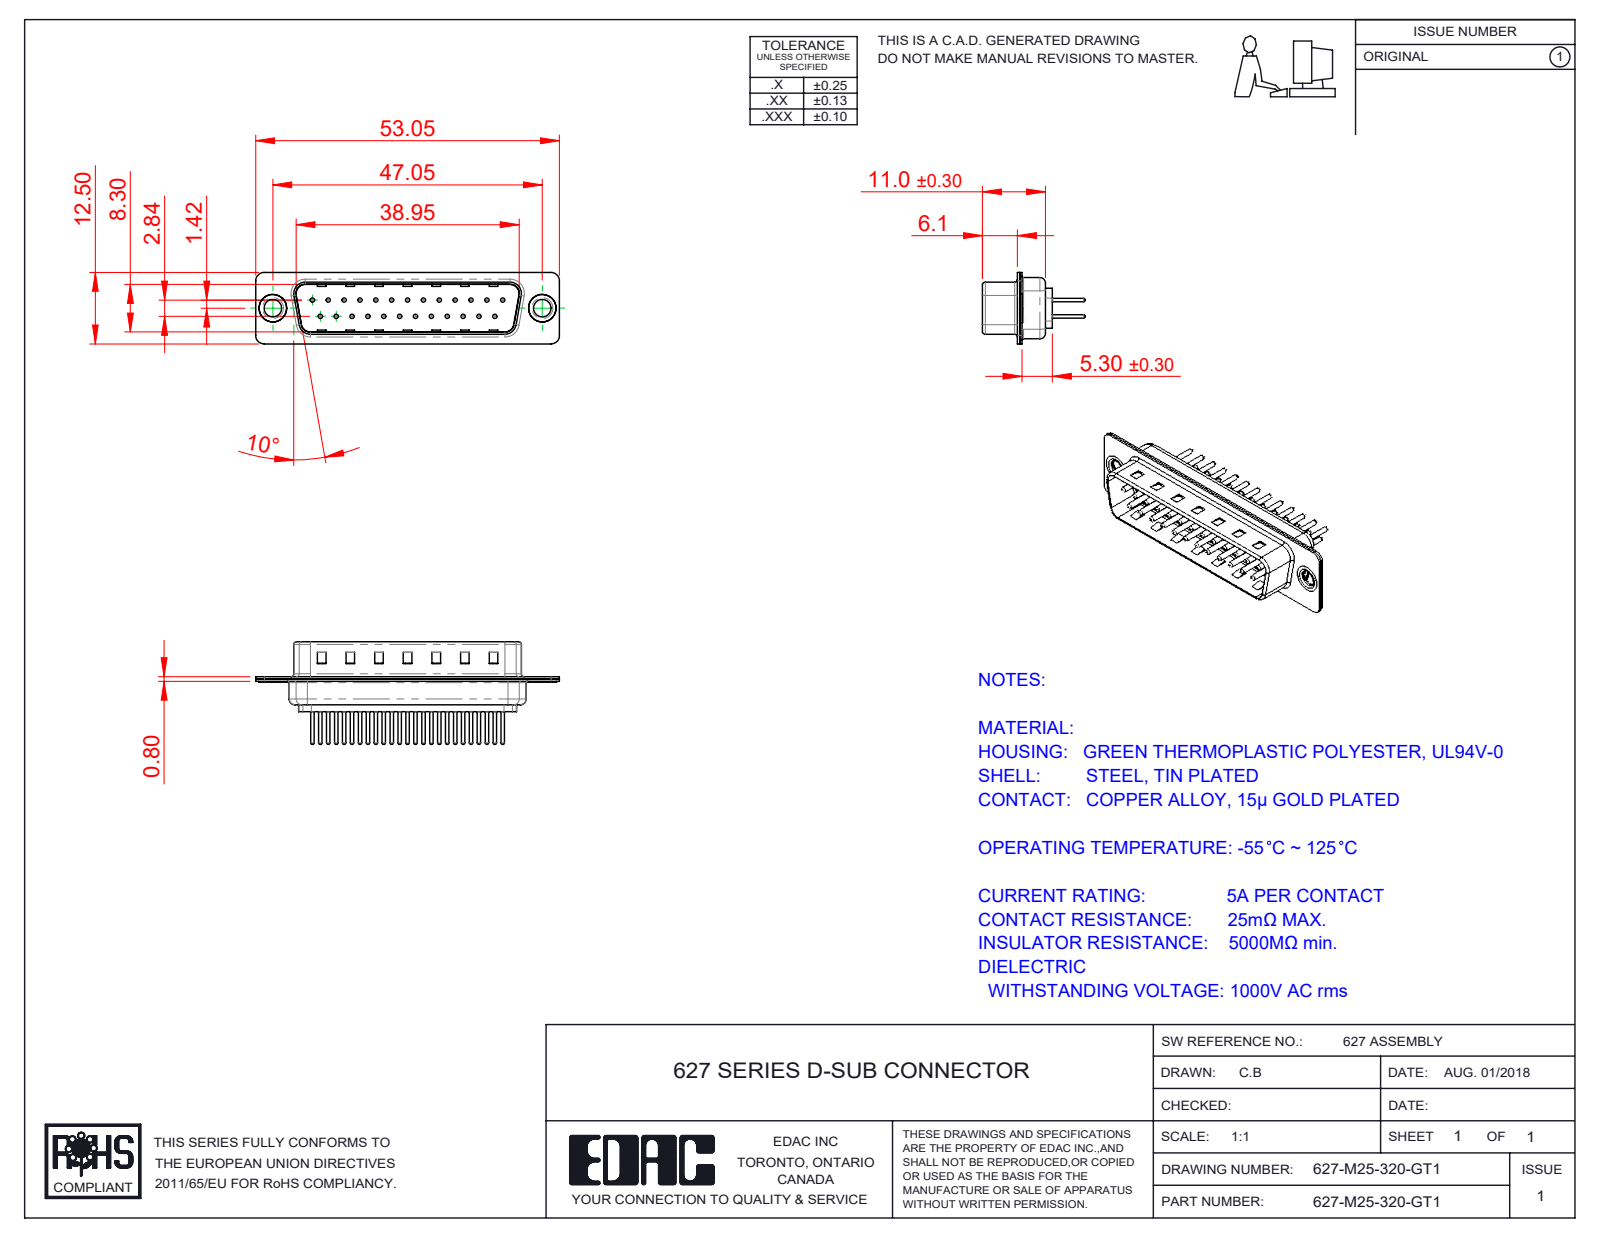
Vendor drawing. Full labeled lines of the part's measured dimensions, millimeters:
Part name (STEP PRODUCT): 627M Shell Front_25 Contacts; 627M Contact Row 2_20; 627M Thru Hole Rivet; 627-M25-320-GT1 (+3 more)
STEP written by: SolidWorks 2020 (CONFIG_CONTROL_DESIGN)
Units: millimetres
Bodies: 30 solids, 1275 faces (346 planar, 471 cylindrical, 458 other)
Overall size (bounding box): 53.05 × 17.9 × 12.5
Volume: 2 641 mm³ · Surface area: 6 698 mm²
Round holes (diameter × count): ⌀0.75 ×25, ⌀1.6 ×25, ⌀2 ×25, ⌀3.05 ×2, ⌀4 ×2, ⌀4.8 ×2
Round bosses / shafts (diameter × count): ⌀1.5 ×25, ⌀0.6 ×25, ⌀5 ×2, ⌀4.9 ×2, ⌀3.55 ×2
Partial cylindrical surfaces — rounded edges, fillets, slot ends (radius × count): R1.5 ×16, R2 ×12, R0.5 ×8, R1.6 ×8, R0.25 ×4, R0.6 ×4, R0.65 ×4, R0.9 ×4
Main face-to-face distances: 0.4, 0.8, 9.5, 9.1, 8.7, 9.9, 1.2, 6.1, 5.7, 0.75
Hole centre spacings: 3.16, 2.77, 5.54, 8.31, 11.08, 13.85, 16.62, 5.03
